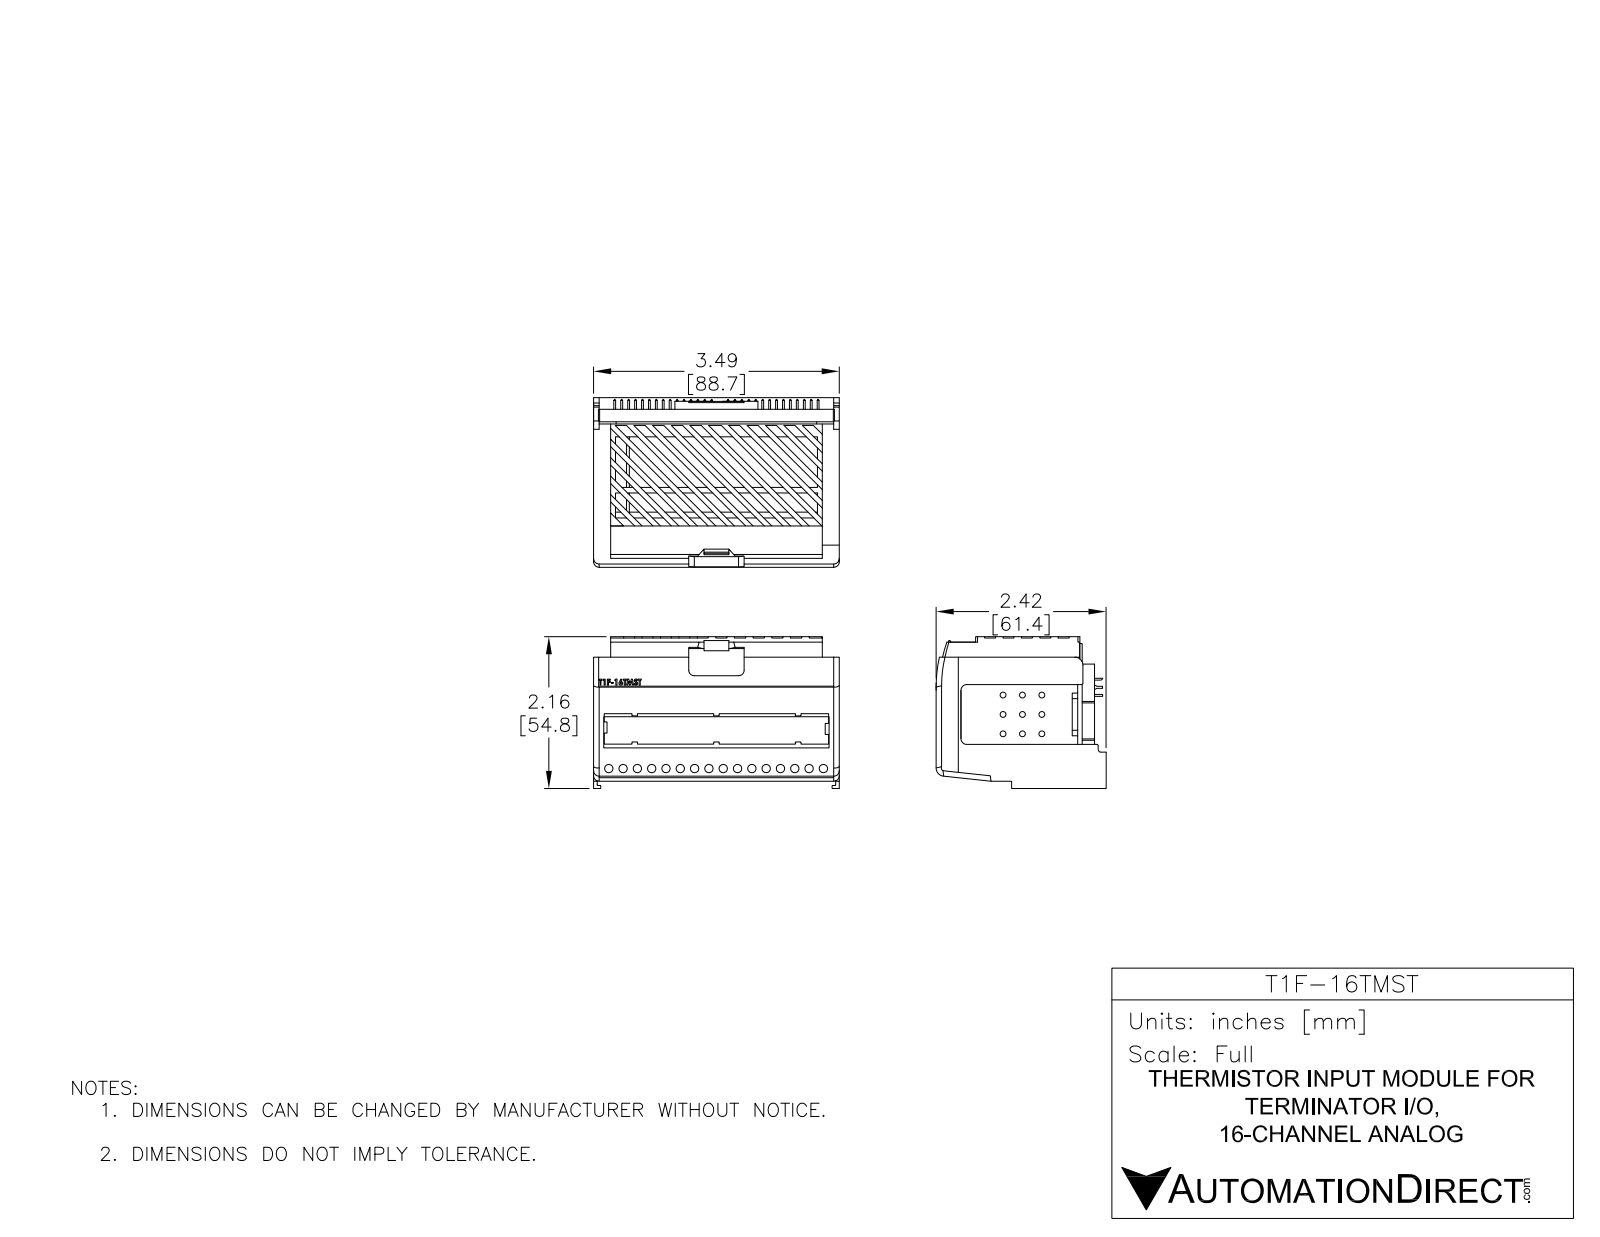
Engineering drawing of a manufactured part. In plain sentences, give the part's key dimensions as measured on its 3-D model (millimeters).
The part is named "T1F-16TMST". Its 3-D file was written by "SolidWorks 2015 (AUTOMOTIVE_DESIGN)". It is 2 solids with 658 faces: 453 planar, 181 cylindrical and 24 other. Overall it measures 88.7 by 61.4 by 54.9 millimeters. Its volume is 39 690 cubic millimeters and its surface area 49 480 square millimeters. Round holes: 16 of diameter 3. Round bosses or shafts: 56 of diameter 0.7. Partial cylindrical surfaces (rounded edges, fillets, slot ends): 18 of radius 3.5, 5 of radius 1, 3 of radius 0.3, 3 of radius 0.6, 2 of radius 1.5, 1 of radius 8, 1 of radius 10, 1 of radius 18. The main face-to-face distances are 2, 86.7, 0.5, 49.6, 55.3, 55.3, 88.7, 1.5, 42.3, 7.4. The hole center spacings are 5.2, 10.3, 15.4, 20.6, 25.8, 30.9, 36, 41.2.
